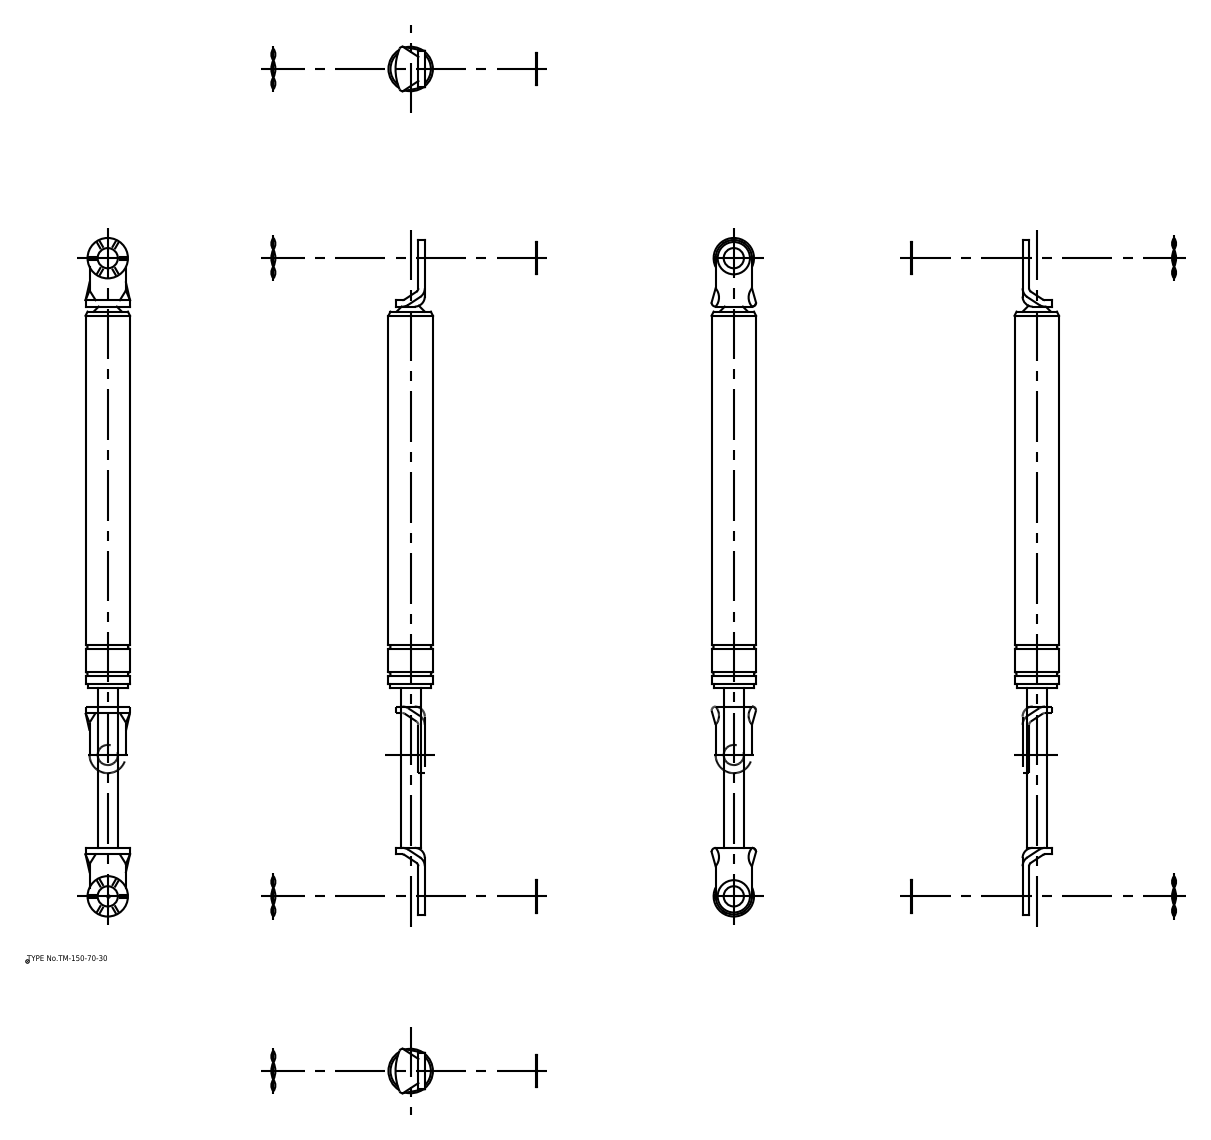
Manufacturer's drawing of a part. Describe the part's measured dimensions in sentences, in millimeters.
The part is named "ウェーブワッシャー; ワッシャー; 本体; 本体_div". Its 3-D file was written by "spGate 16.7.1 (AUTOMOTIVE_DESIGN)". It is 6 solids with 94 faces: 42 planar, 44 cylindrical and 8 other. Overall it measures 336 by 22.5 by 22.5 millimeters. Its volume is 82 809 cubic millimeters and its surface area 21 827 square millimeters. Round holes: 2 of diameter 10. Round bosses or shafts: 3 of diameter 20, 2 of diameter 16, 1 of diameter 22.5, 1 of diameter 22, 1 of diameter 10. Partial cylindrical surfaces (rounded edges, fillets, slot ends): 2 of radius 4.4, 2 of radius 5, 2 of radius 9, 1 of radius 26.32. The main face-to-face distances are 3.2, 2, 5.2, 271.2, 5.7, 3.7, 0.5, 192.2, 82.2, 274.4. The hole center spacings are 316.
